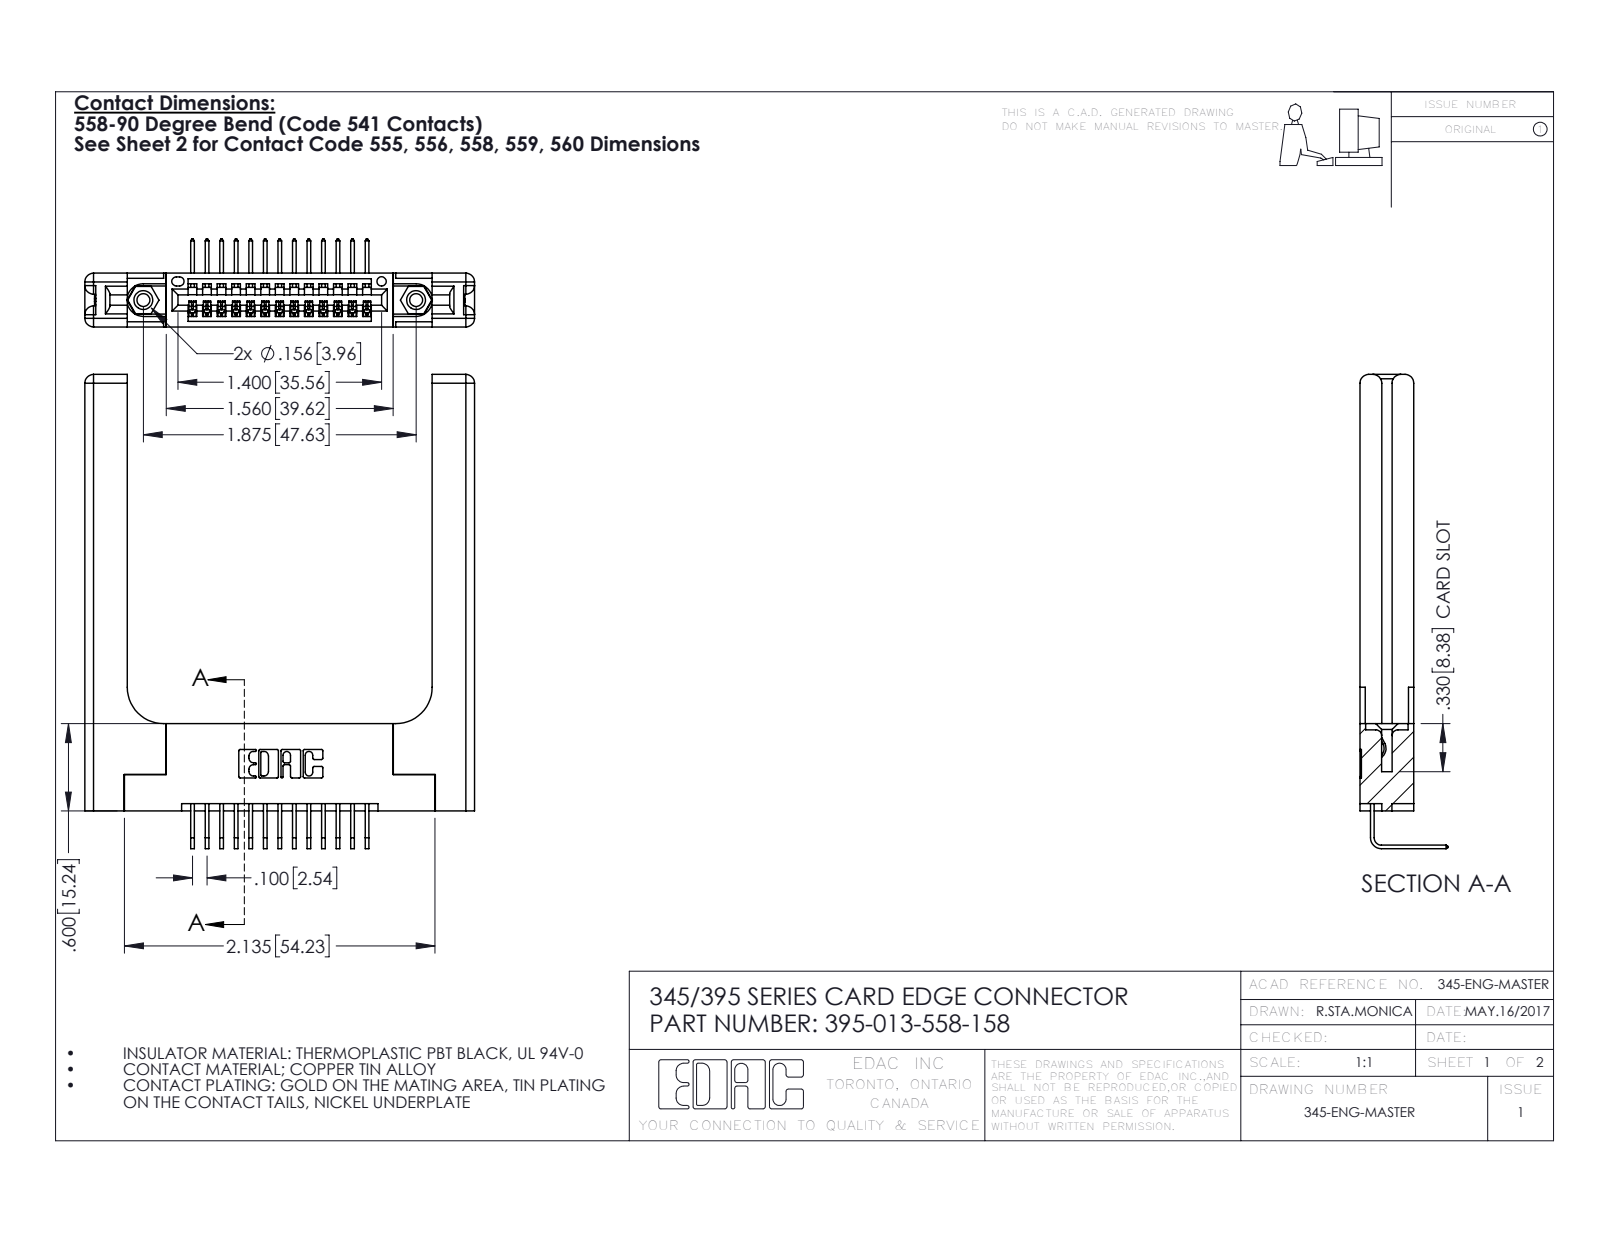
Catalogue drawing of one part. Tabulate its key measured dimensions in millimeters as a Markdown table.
| quantity | value |
| --- | --- |
| part name | 345 Part_Flush Mounting Lugs - 0.156 Dia-TH; 345-250-001_345-250-001-102; 395-013-558-158; 345-220-058_345-220-058 (+1 more) |
| STEP written by | SolidWorks 2016 (CONFIG_CONTROL_DESIGN) |
| units | millimeters |
| bodies | 18 solids, 1162 faces (774 planar, 328 cylindrical, 60 other) |
| overall size | 82.8 × 68 × 15.4 |
| volume | 14 800 mm³ |
| surface area | 13 500 mm² |
| round holes (diameter × count) | 2.3 × 2, 3.2 × 2, 4 × 2, 1.6 × 1 |
| round bosses / shafts (diameter × count) | 3.9 × 2 |
| partial cylindrical surfaces (radius × count) | 0.2 × 26, 0.3 × 22, 1.5 × 16, 0.2 × 6, 0.8 × 6, 0.7 × 3, 0.8 × 2, 0.8 × 2 |
| main face-to-face distances | 9.4, 1.8, 3.8, 7.6, 2, 3.8, 5.6, 5.1, 53.2, 2.5 |
| hole center spacings | 6.9, 41.7, 47.6 |
